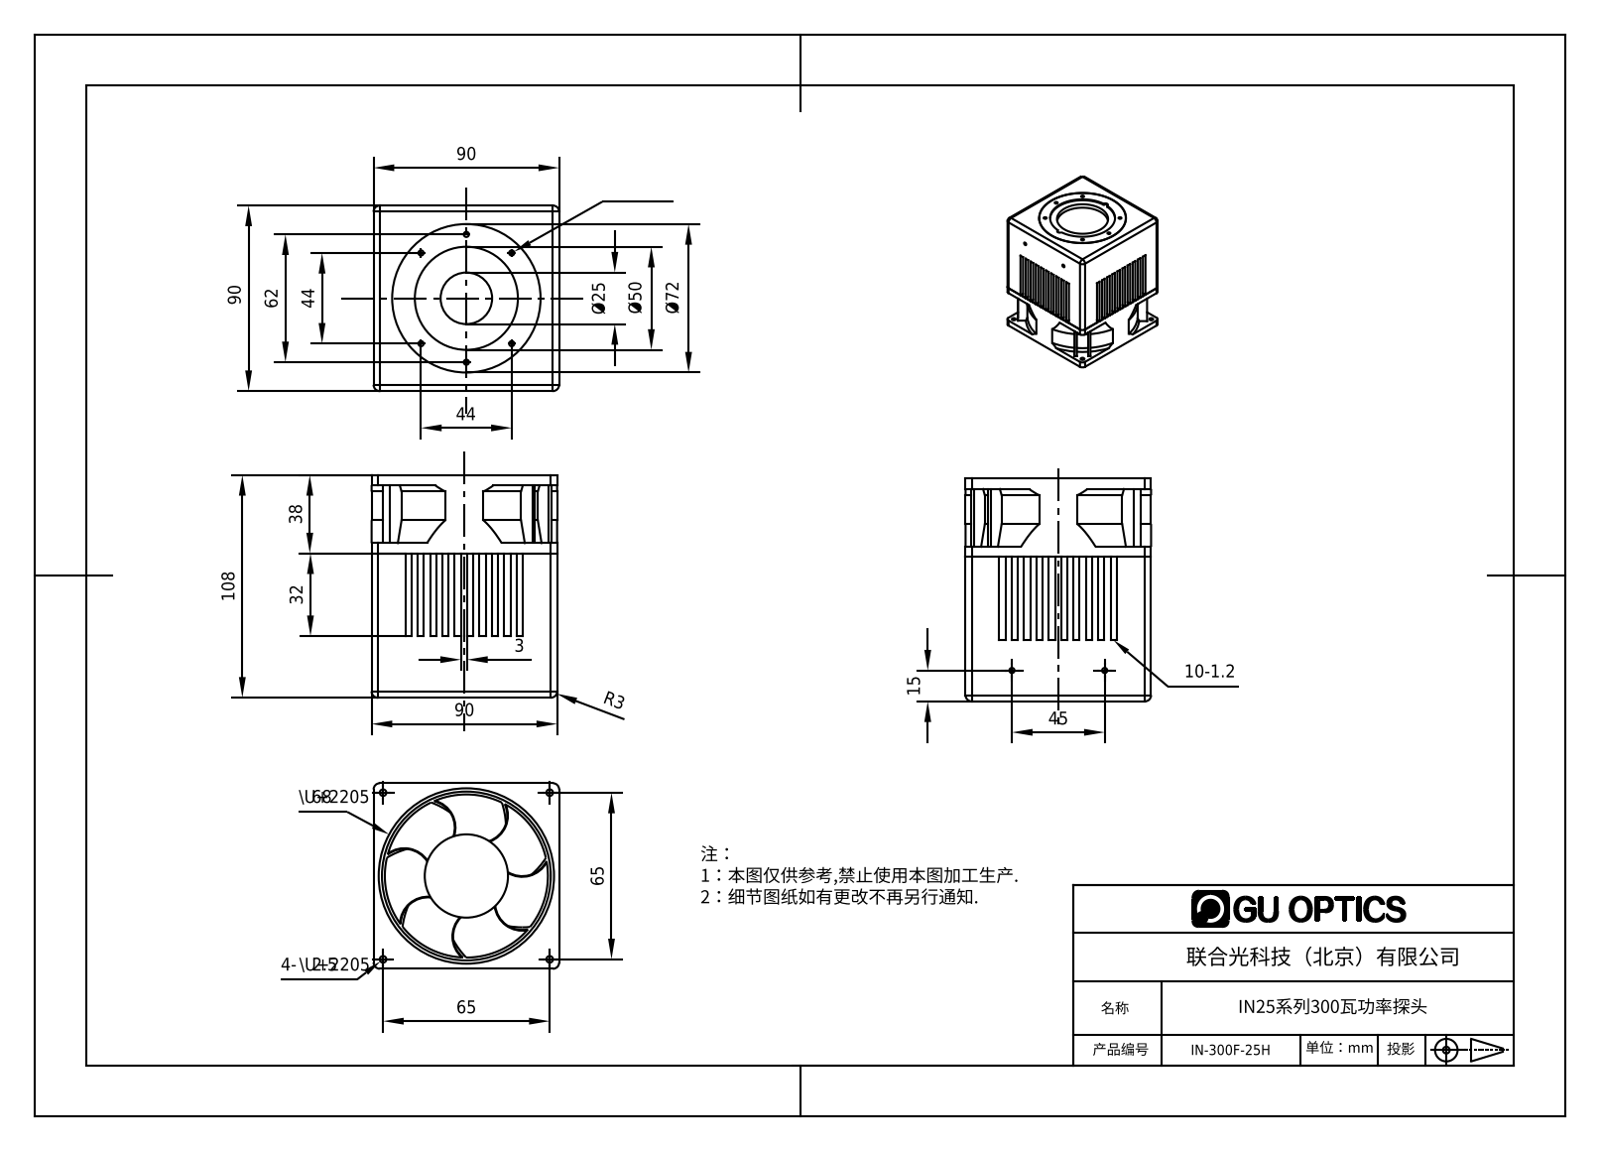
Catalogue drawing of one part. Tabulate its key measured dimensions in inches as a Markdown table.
| quantity | value |
| --- | --- |
| part name | 200W̽ͷ |
| STEP written by | SolidWorks 2020 (CONFIG_CONTROL_DESIGN) |
| units | inches |
| bodies | 9 solids, 240 faces (101 planar, 83 cylindrical, 56 other) |
| overall size | 4.252 × 3.543 × 3.543 |
| volume | 36.51 in³ |
| surface area | 282.3 in² |
| round holes (diameter × count) | 0.098 × 8, 0.126 × 4, 0.984 × 1, 1.969 × 1, 2.843 × 1, 3.224 × 1, 3.349 × 1 |
| round bosses / shafts (diameter × count) | 3.114 × 1, 2.835 × 1, 1.59 × 1 |
| partial cylindrical surfaces (radius × count) | 0.118 × 8, 1.809 × 1 |
| main face-to-face distances | 0.118, 0.236, 0.354, 0.472, 0.591, 0.709, 0.827, 0.945, 1.063, 1.181 |
| hole center spacings | 2.562, 0.936, 1.026, 1.225, 1.634, 1.732, 2.25, 2.259 |
